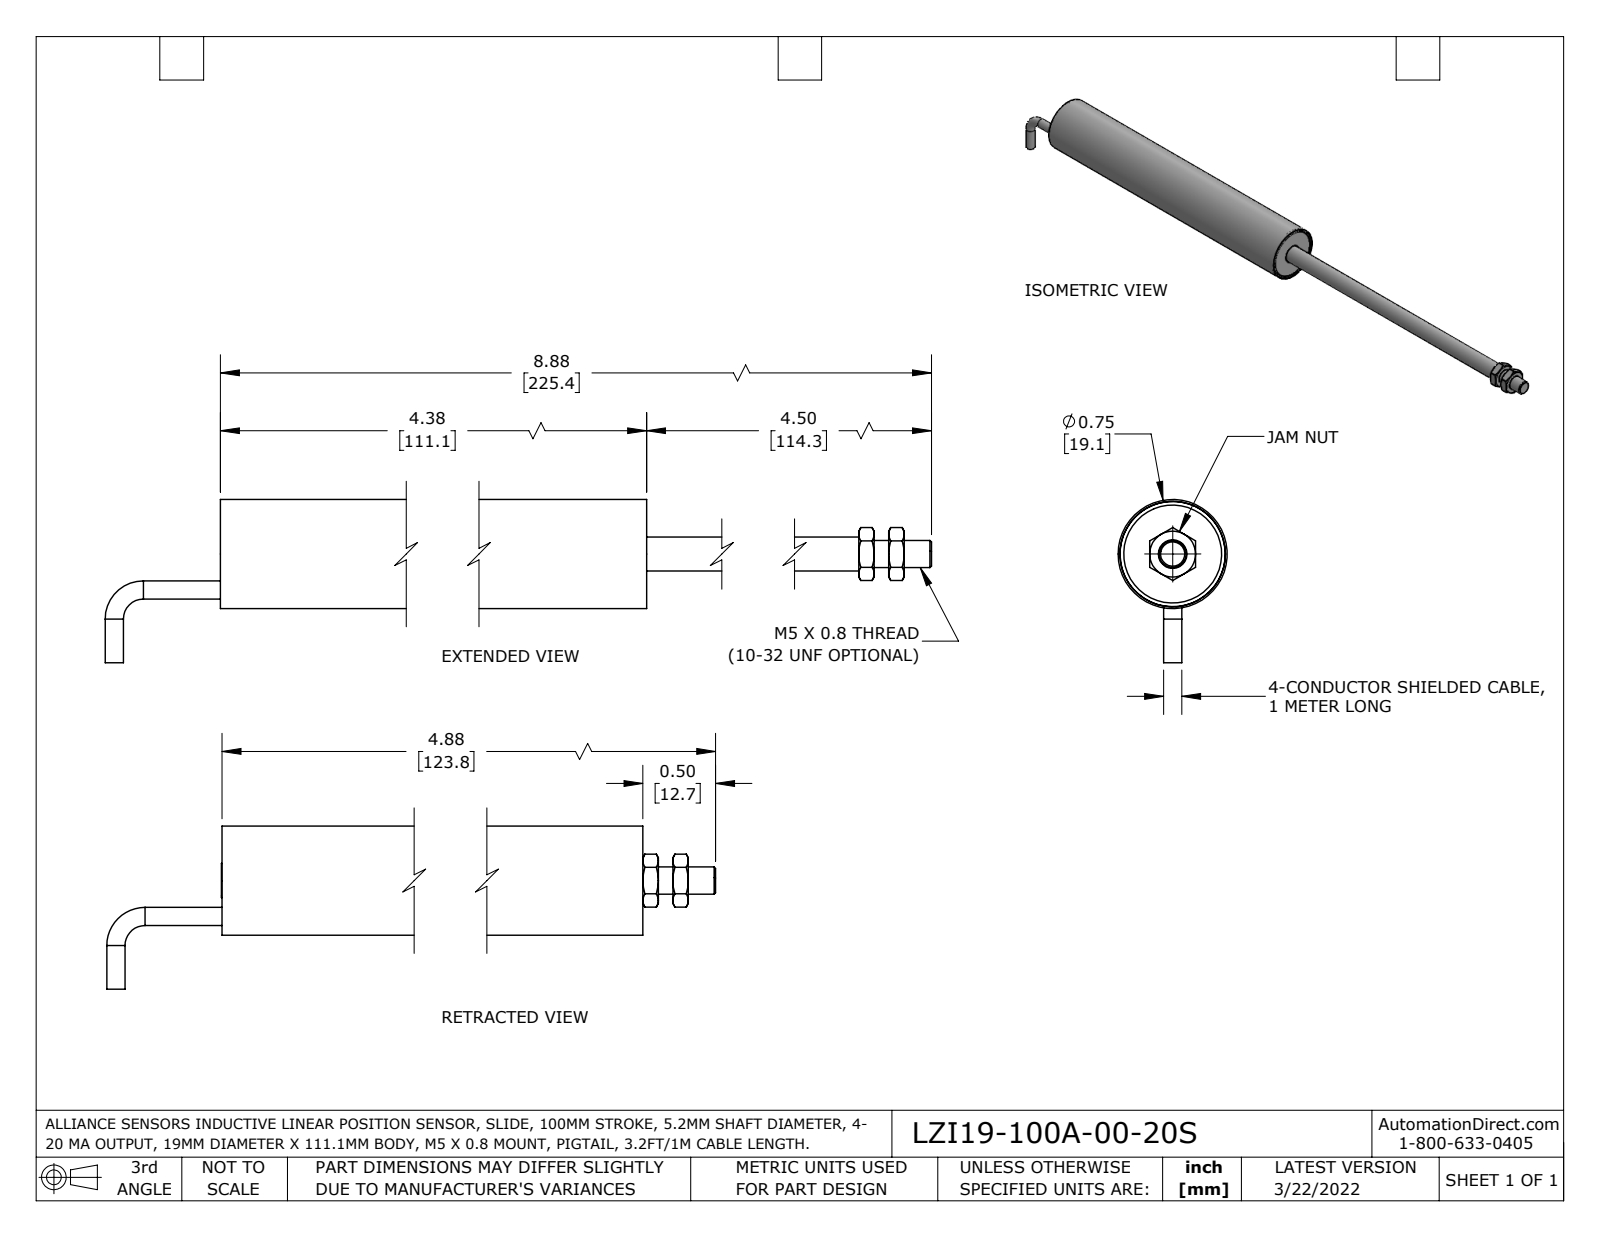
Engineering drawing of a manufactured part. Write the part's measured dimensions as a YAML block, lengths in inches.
part_name: "3120-0007-ZY_with slot; 3120-0007-ZY; 3300-0008-06_-04; 3100-0076_B18.2.4.5M - Hex jam nut, M5 x 0.8 --D-N (+6 more)"
step_written_by: "SolidWorks 2021 (AUTOMOTIVE_DESIGN)"
units: inches
bodies: {solids: 10, faces: 137, planar: 42, cylindrical: 44, other: 51}
overall_size: [9.668, 1.121, 0.75]
volume: 0.717
surface_area: 39.5
round_holes:
  - {diameter: 0.165, count: 1}
  - {diameter: 0.188, count: 1}
  - {diameter: 0.197, count: 1}
  - {diameter: 0.234, count: 1}
  - {diameter: 0.281, count: 1}
  - {diameter: 0.68, count: 1}
  - {diameter: 0.725, count: 1}
round_bosses_or_shafts:
  - {diameter: 0.125, count: 2}
  - {diameter: 0.75, count: 1}
  - {diameter: 0.723, count: 1}
  - {diameter: 0.278, count: 1}
  - {diameter: 0.187, count: 1}
partial_cylinders:
  - {radius: 0.052, count: 1}
face_to_face_distances: [0.06, 4.295, 0.08, 4.235, 4.355, 0.315, 0.206, 0.106, 0.374, 0.03]
